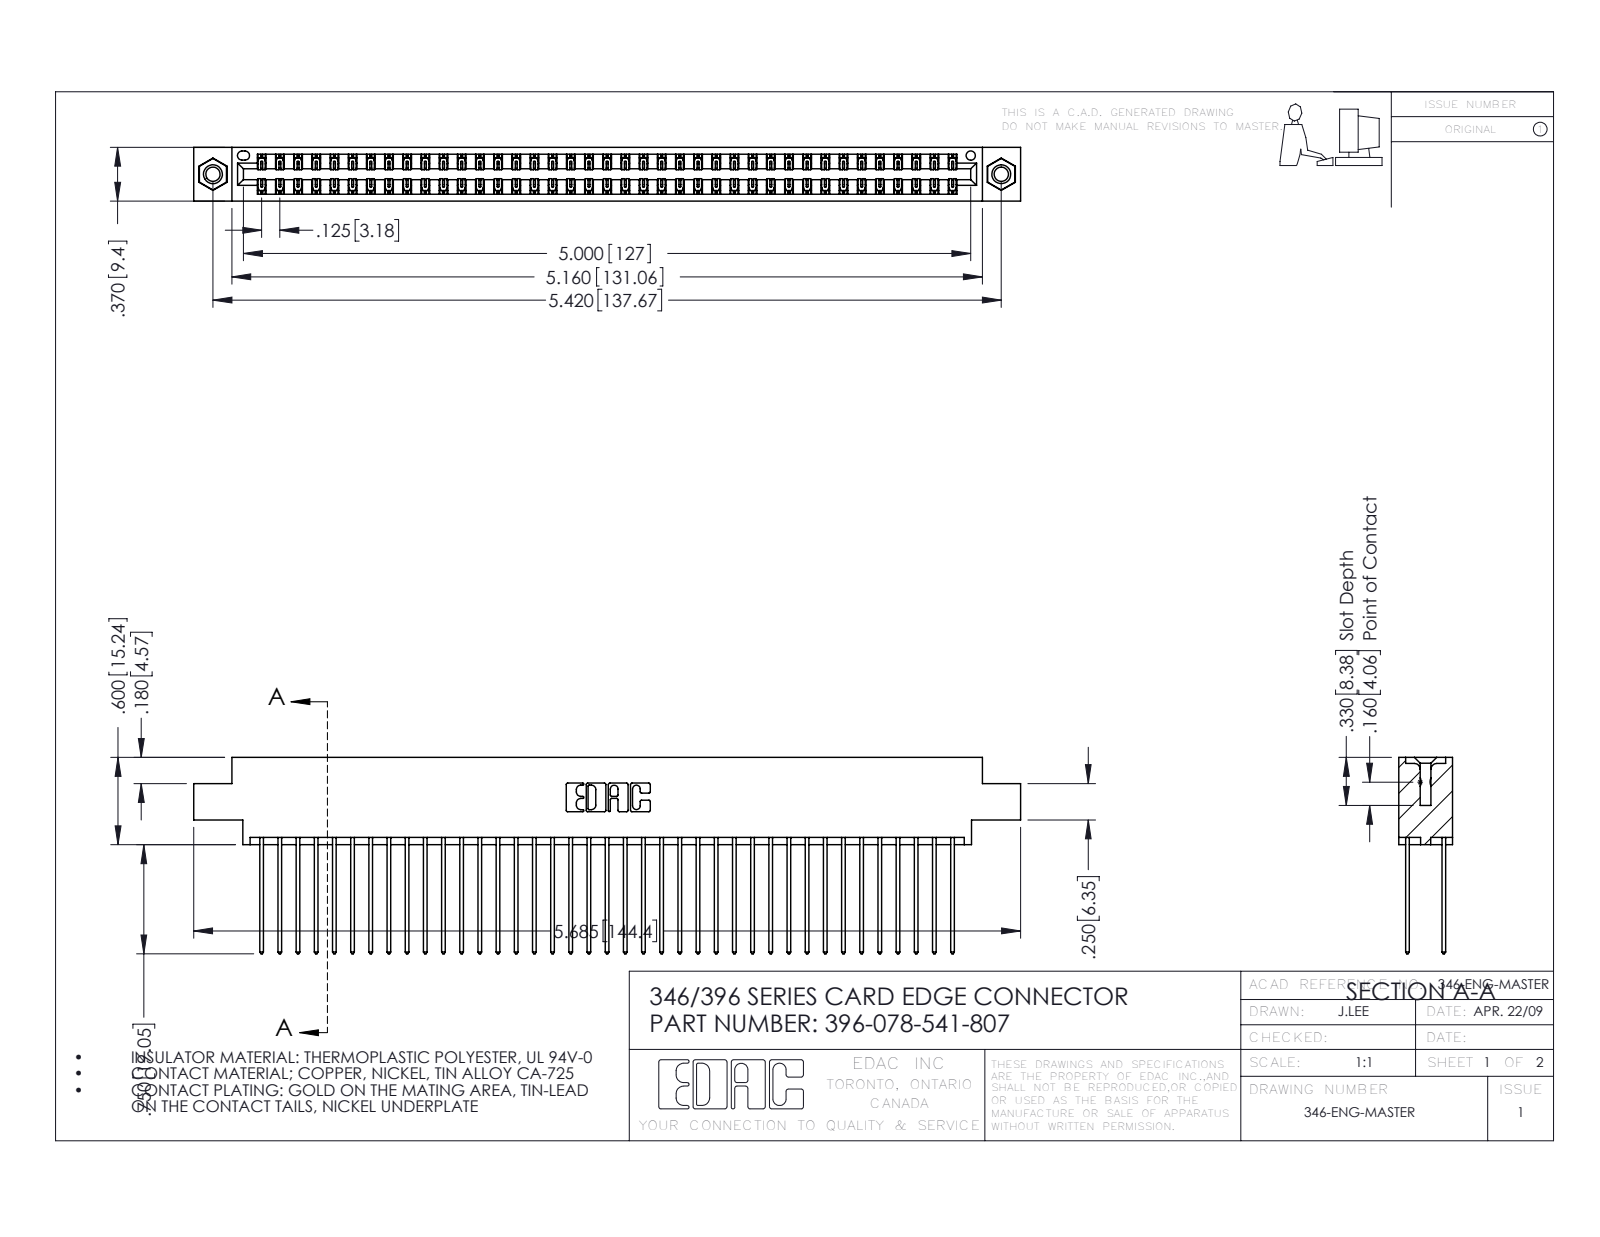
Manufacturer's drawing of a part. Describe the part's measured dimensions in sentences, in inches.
The part is named "345-250-001_345-250-005-103; 345-292-001_345-293-141; 346 Part_0.170 Offset - 0.156 Dia-TI; 396-078-541-807". Its 3-D file was written by "SolidWorks 2016 (CONFIG_CONTROL_DESIGN)". It is 81 solids with 4242 faces: 2842 planar, 1384 cylindrical and 16 other. Overall it measures 5.685 by 1.35 by 0.37 inches. Its volume is 0.875 cubic inches and its surface area 34.13 square inches. Round holes: 2 of diameter 0.098, 2 of diameter 0.125, 2 of diameter 0.156, 1 of diameter 0.064. Round bosses or shafts: 2 of diameter 0.155. Partial cylindrical surfaces (rounded edges, fillets, slot ends): 117 of radius 0.006, 78 of radius 0.01, 22 of radius 0.01, 6 of radius 0.007, 6 of radius 0.031, 3 of radius 0.026, 2 of radius 0.014, 2 of radius 0.022. The main face-to-face distances are 0.048, 0.322, 0.25, 0.072, 0.298, 0.025, 0.37, 0.275, 0.225, 0.222. The hole center spacings are 0.246, 5.211, 5.42.
